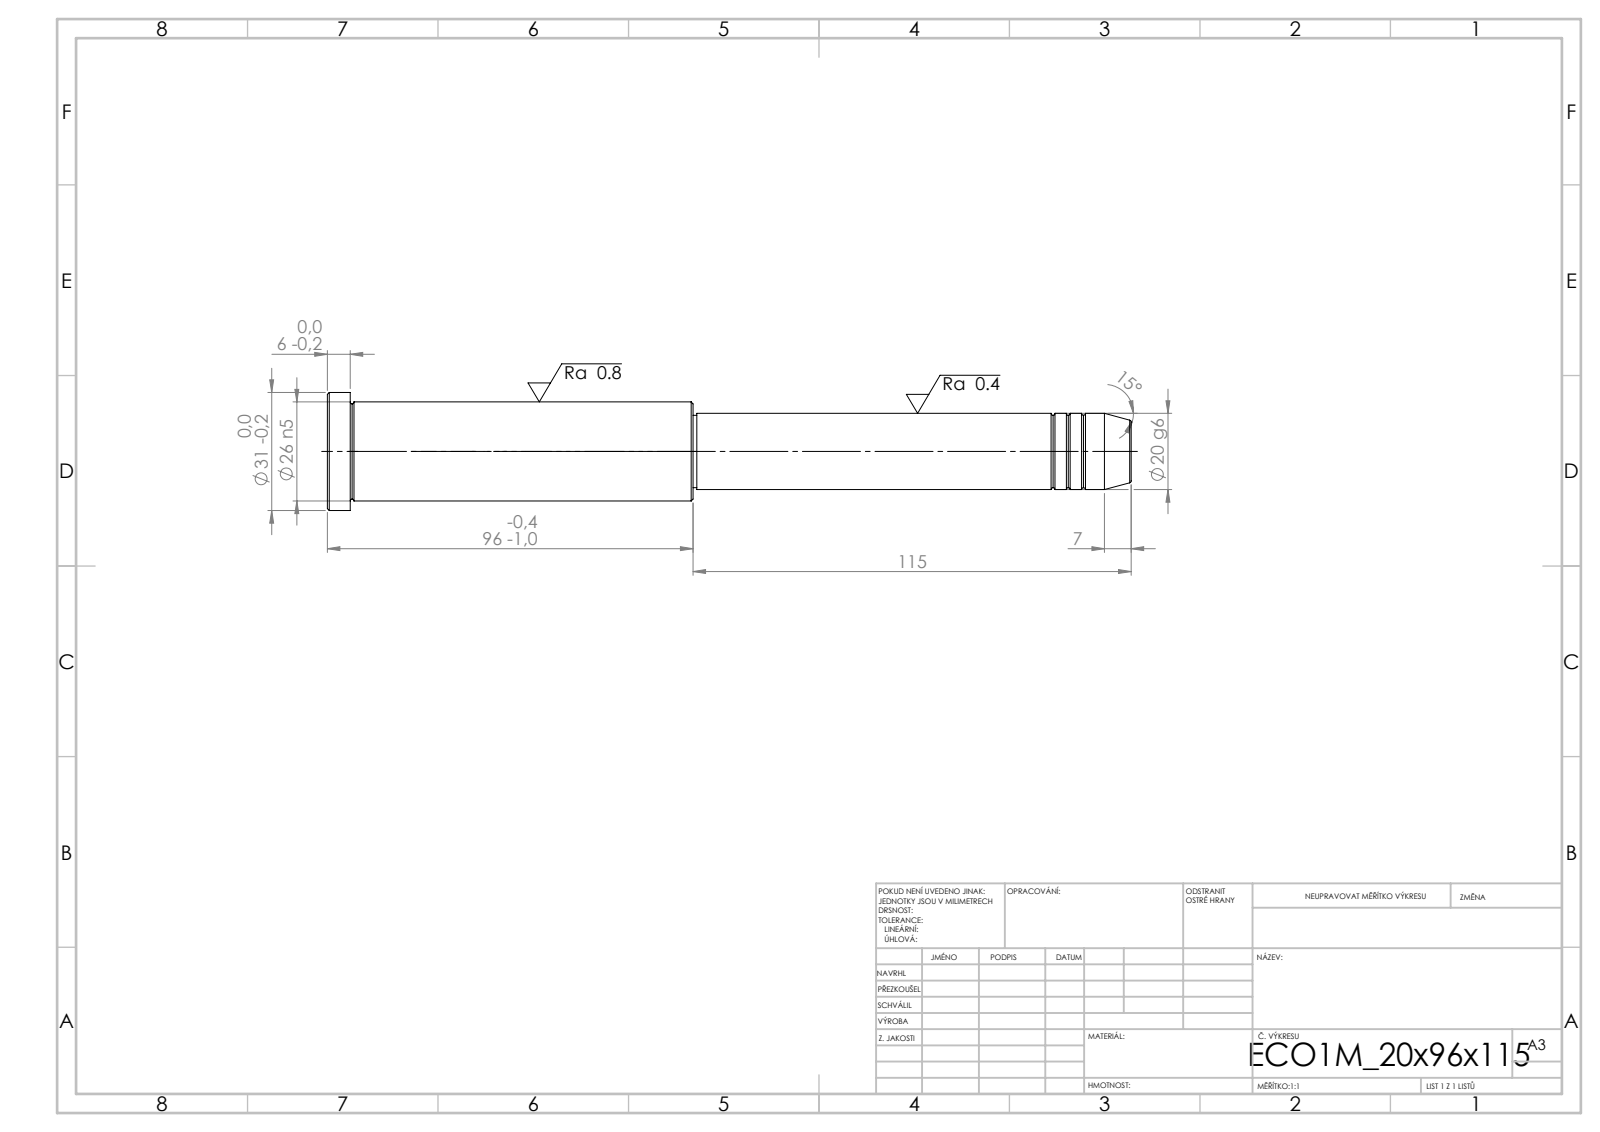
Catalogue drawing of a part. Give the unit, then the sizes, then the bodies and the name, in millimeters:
Units: millimetres
Overall size (bounding box): 211 × 31 × 31
Round bosses / shafts (diameter × count): ⌀31 ×1, ⌀26 ×1, ⌀20 ×1, ⌀19 ×1
Main face-to-face distances: 6, 90, 96, 115, 205, 211, 114, 1, 91, 97
Volume: 87 896 mm³ · Surface area: 16 678 mm²
Bodies: 1 solid, 43 faces (5 planar, 14 cylindrical, 24 other)
STEP written by: SolidWorks 2019 (CONFIG_CONTROL_DESIGN)
